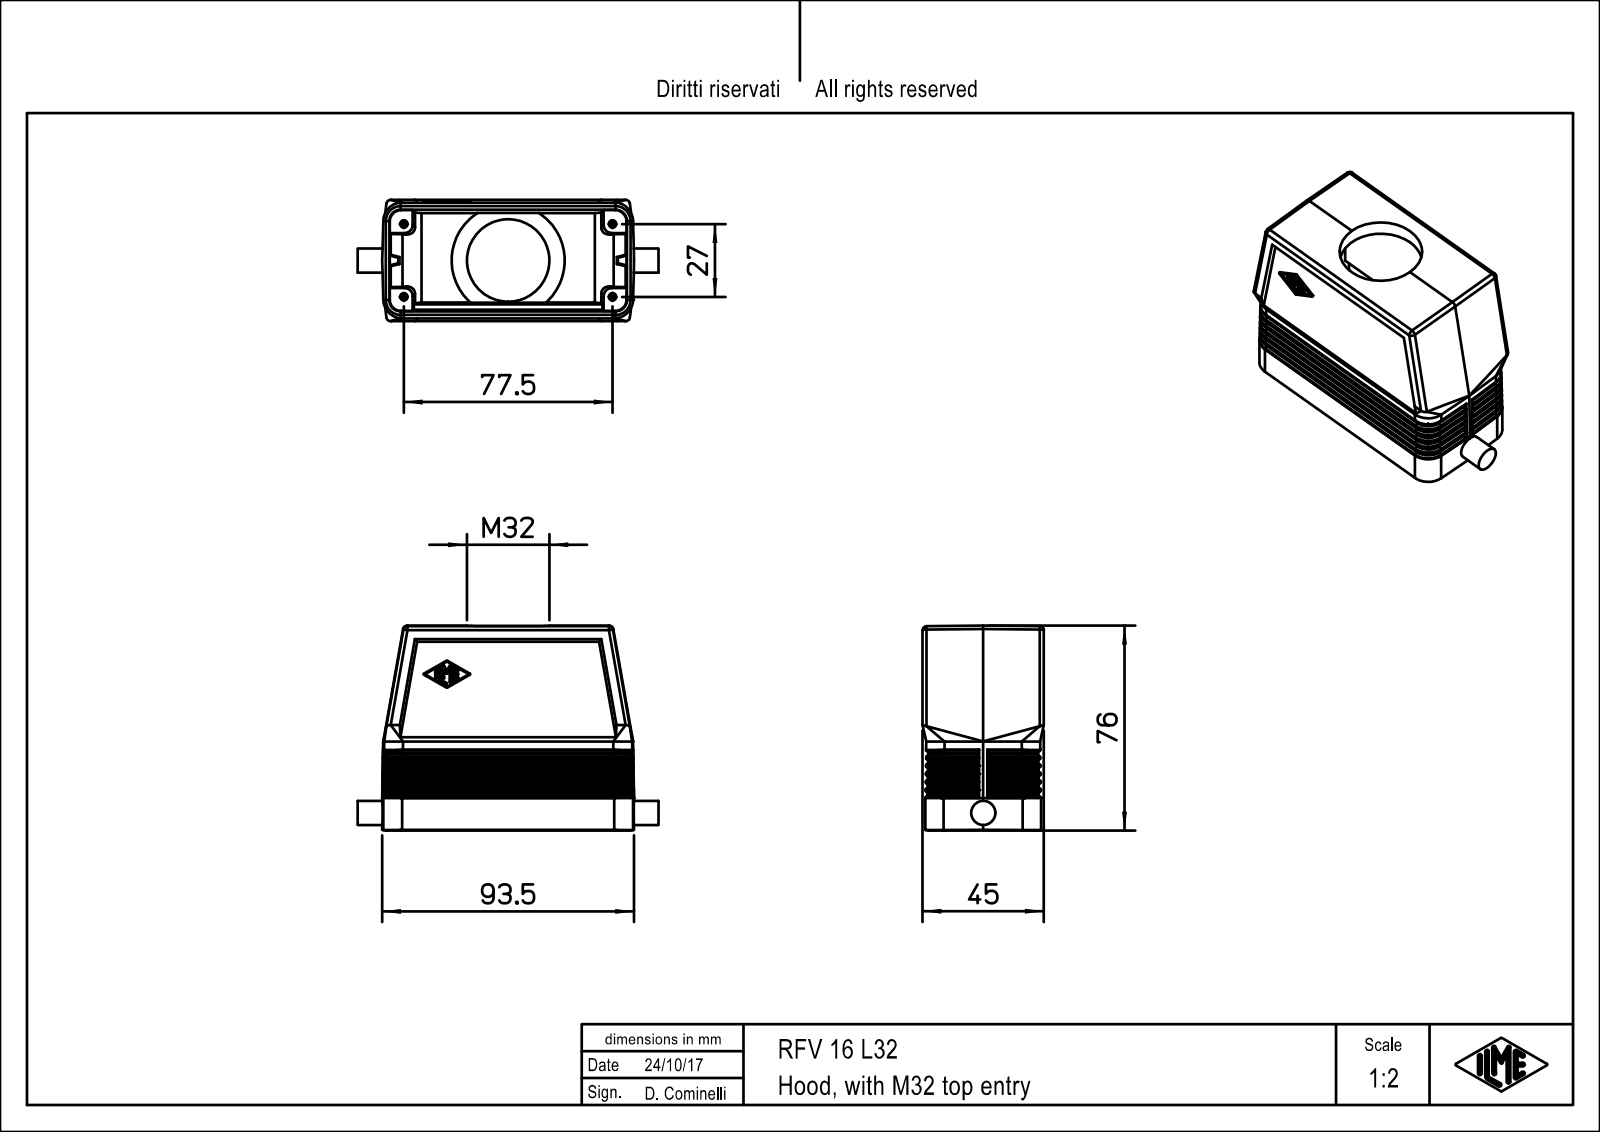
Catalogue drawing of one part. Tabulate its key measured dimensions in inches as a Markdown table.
| quantity | value |
| --- | --- |
| part name | RFV_16_L32 |
| STEP written by | PTC Creo Elements/Direct Modeling 19.0E 27-Jun-2016 (C) Parametric Technology GmbH (AUTOMOTIVE_DESIGN) |
| units | inches |
| bodies | 1 solid, 511 faces (236 planar, 139 cylindrical, 136 other) |
| overall size | 4.398 × 2.992 × 1.772 |
| volume | 5.498 in³ |
| surface area | 67.99 in² |
| round holes (diameter × count) | 1.205 × 1 |
| round bosses / shafts (diameter × count) | 0.354 × 1 |
| partial cylindrical surfaces (radius × count) | 0.02 × 78, 0.013 × 15, 0.059 × 10, 0.276 × 8, 0.118 × 4, 0.165 × 4, 0.007 × 3, 0.026 × 1 |
| main face-to-face distances | 1.693, 0.079, 0.079, 0.335, 0.157, 0.039, 1.732, 0.236, 0.237, 0.126 |
